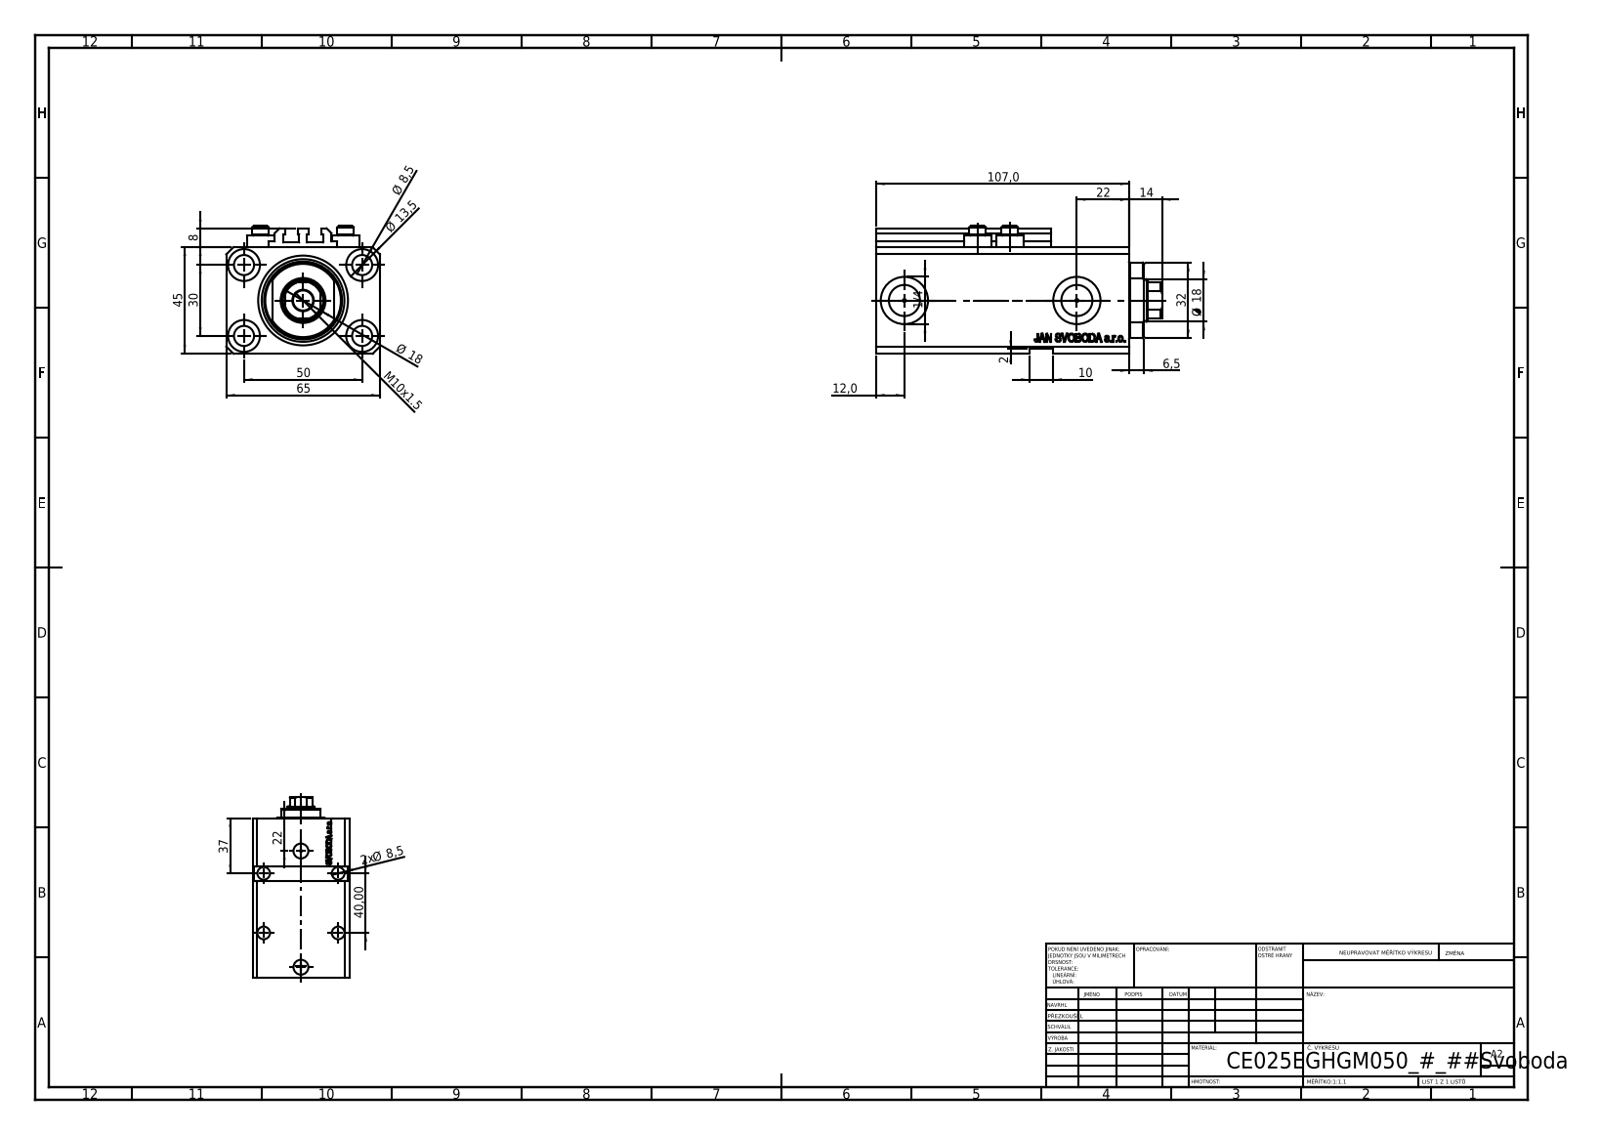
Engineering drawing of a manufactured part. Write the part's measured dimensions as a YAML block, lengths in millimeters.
part_name: "V250CE_VC_E; V250CE_E_Body; ALLEN BOLT V250CE; V250CE_C_VCP"
step_written_by: "SolidWorks 2019 (CONFIG_CONTROL_DESIGN)"
units: millimeters
bodies: {solids: 8, faces: 1087, planar: 511, cylindrical: 146, other: 430}
overall_size: [121, 65, 54]
volume: 273399
surface_area: 76876
round_holes:
  - {diameter: 8.5, count: 9}
  - {diameter: 1.25, count: 4}
  - {diameter: 4, count: 4}
  - {diameter: 13.5, count: 4}
  - {diameter: 10, count: 2}
  - {diameter: 13.16, count: 2}
  - {diameter: 20, count: 2}
  - {diameter: 18, count: 1}
  - {diameter: 25, count: 1}
  - {diameter: 38, count: 1}
round_bosses_or_shafts:
  - {diameter: 11.6, count: 4}
  - {diameter: 7, count: 4}
partial_cylinders:
  - {radius: 0.2, count: 10}
  - {radius: 8.5, count: 1}
  - {radius: 16, count: 1}
face_to_face_distances: [45, 65, 93, 2, 14, 47, 107, 2.5, 10, 20.5]
hole_center_spacings: [29.15, 50, 13.6, 14.76, 15.12, 27.51, 27.89, 30]
